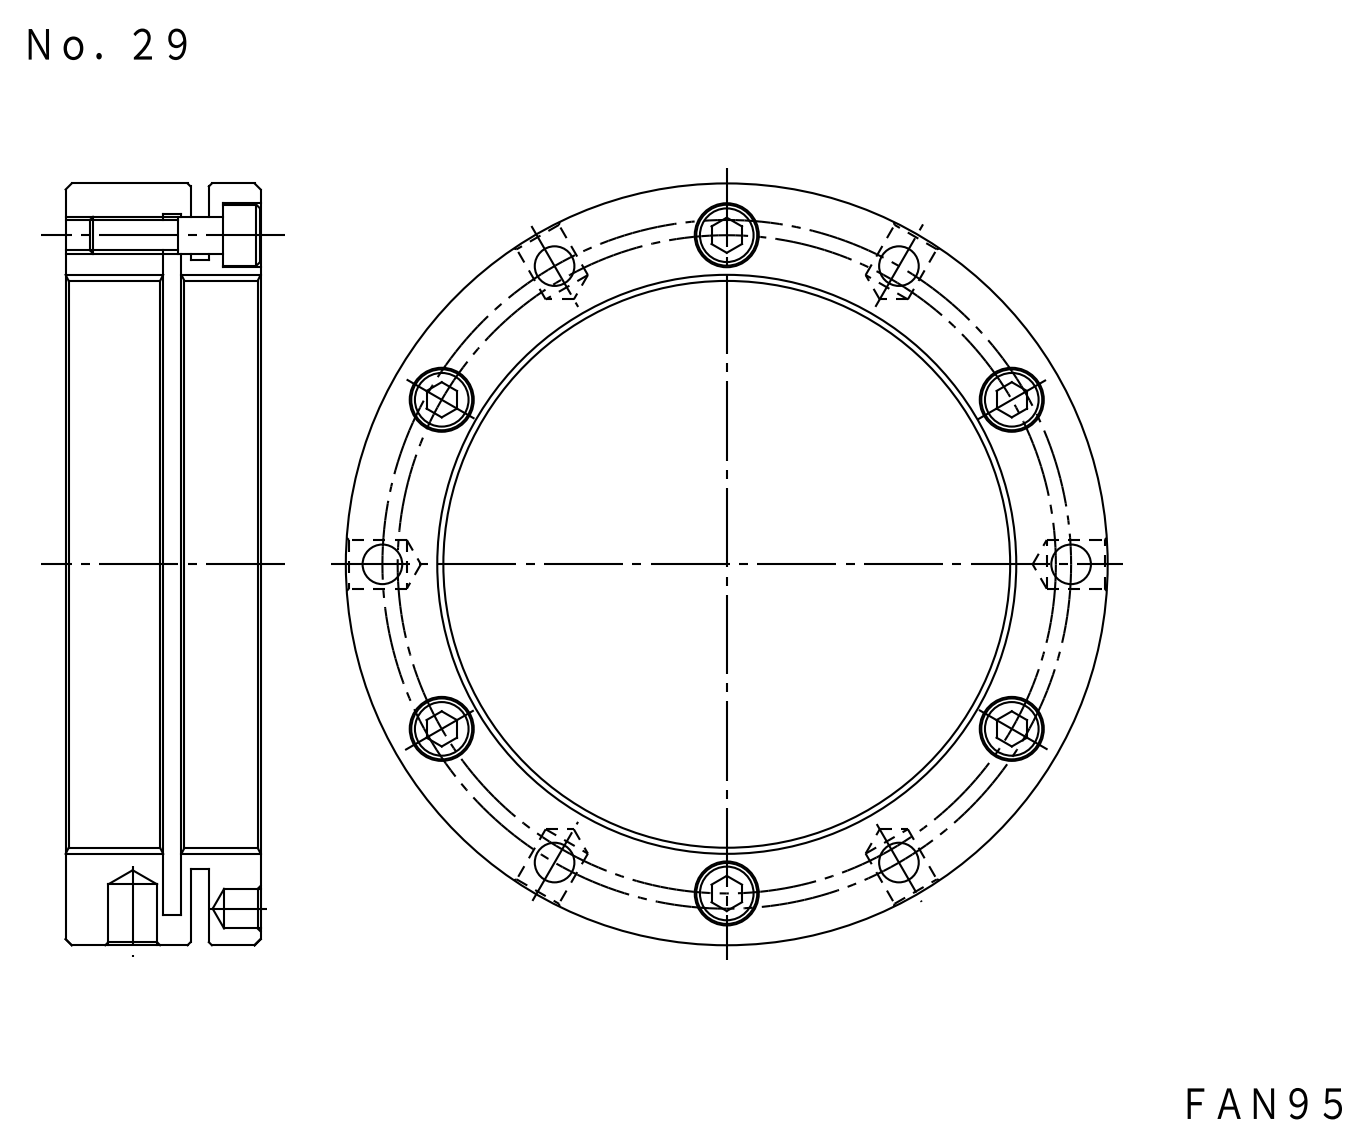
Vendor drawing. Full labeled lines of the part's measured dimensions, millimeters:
Part name (STEP PRODUCT): FKD FAN95; M6X22_default
STEP written by: SolidWorks 2012 (CONFIG_CONTROL_DESIGN)
Units: millimetres
Bodies: 7 solids, 204 faces (72 planar, 108 cylindrical, 24 other)
Overall size (bounding box): 125 × 125 × 32
Volume: 143 310 mm³ · Surface area: 56 790 mm²
Round holes (diameter × count): ⌀6.3 ×6, ⌀6.5 ×6, ⌀10.5 ×6, ⌀4.92 ×3, ⌀4.92 ×3, ⌀8 ×3, ⌀95 ×1, ⌀118 ×1
Round bosses / shafts (diameter × count): ⌀10 ×6, ⌀6 ×6, ⌀125 ×1, ⌀104 ×1
Main face-to-face distances: 2.5, 4, 32, 17, 15, 19.5, 12.5, 21, 1.5, 11
Hole centre spacings: 55.5, 56.5, 108.18, 29, 79.2, 97.86, 29.01, 79.19
